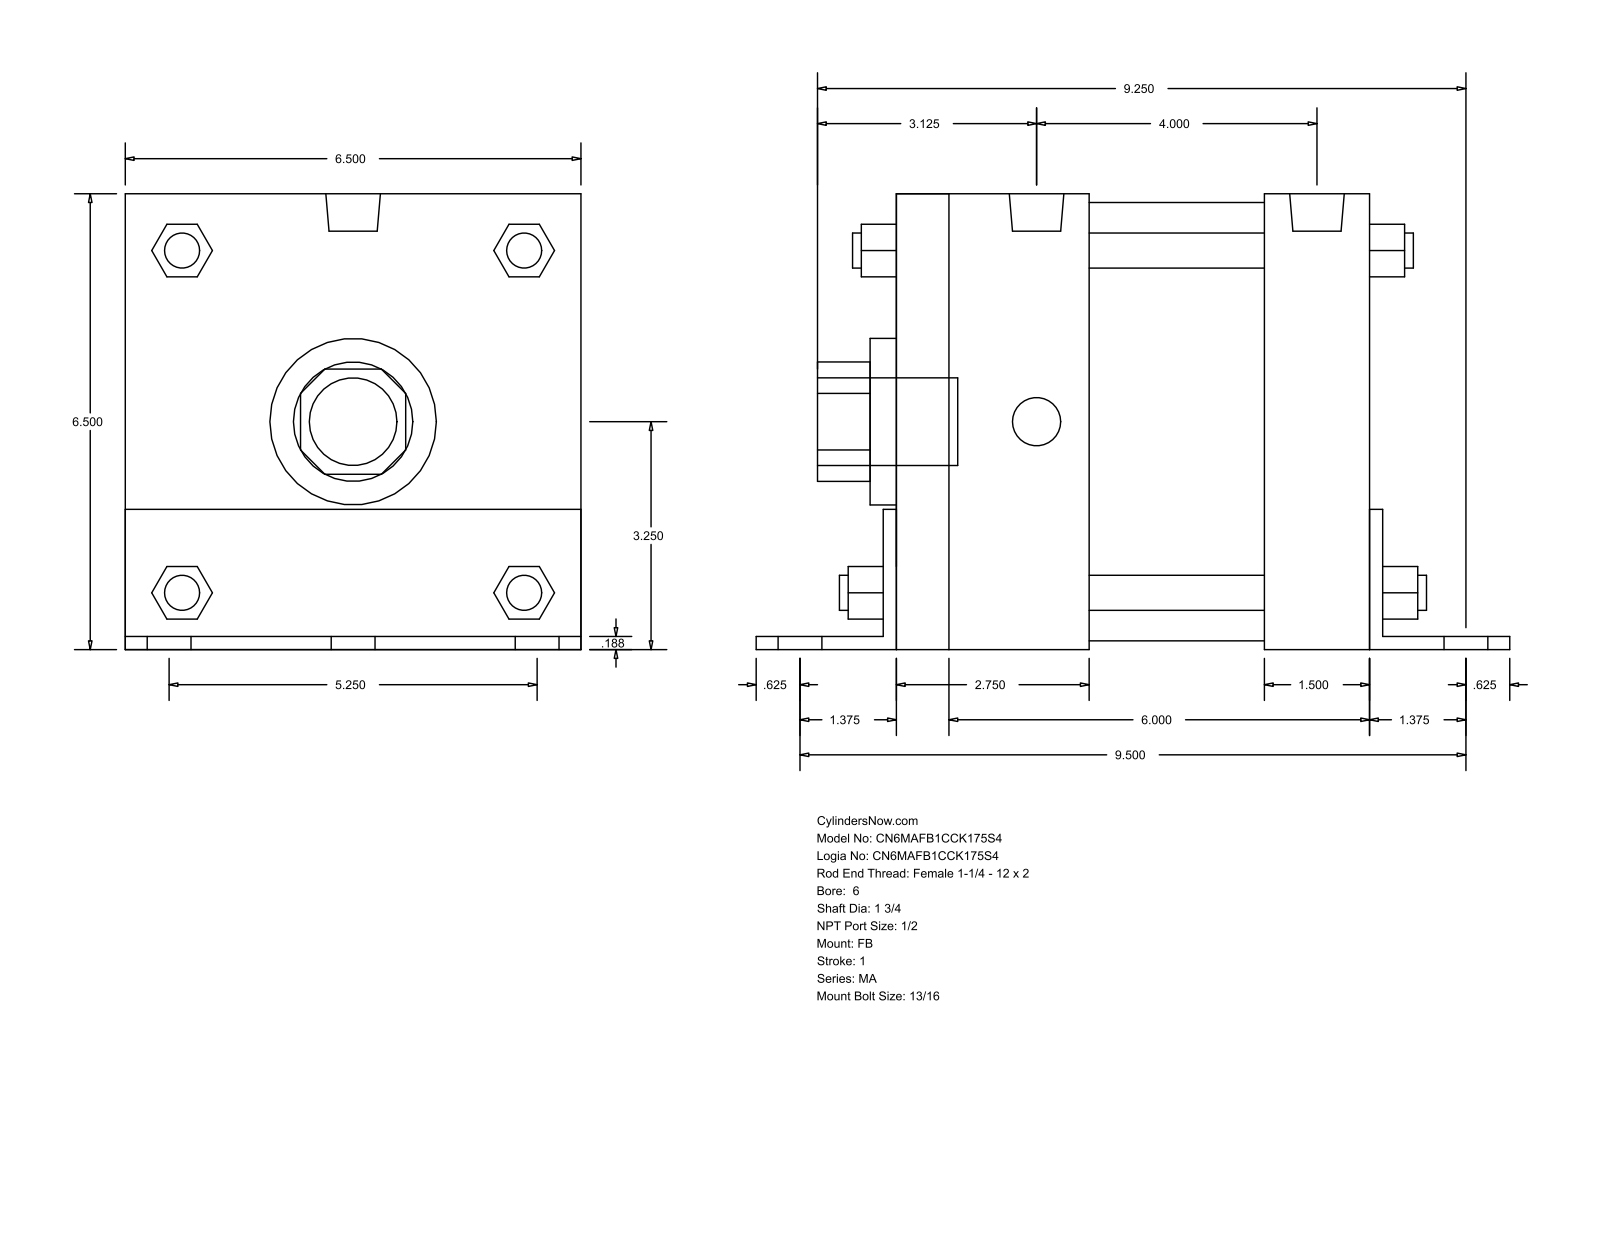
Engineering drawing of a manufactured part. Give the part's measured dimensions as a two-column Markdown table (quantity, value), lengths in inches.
| quantity | value |
| --- | --- |
| part name | MA_FB__0600_1.75 |
| STEP written by | GSSL Pune (CONFIG_CONTROL_DESIGN) |
| units | inches |
| bodies | 0 solids, 140 faces (105 planar, 35 cylindrical, 0 other) |
| overall size | 10.75 × 6.502 × 6.5 |
| round holes (diameter × count) | 1.75 × 1, 2.375 × 1, 6.25 × 1 |
| round bosses / shafts (diameter × count) | 0.813 × 6, 0.687 × 4, 0.5 × 4, 0.778 × 2, 1.25 × 1 |
| partial cylindrical surfaces (radius × count) | 0.852 × 1, 1.262 × 1 |
| main face-to-face distances | 6.5, 0.187, 6.75, 6.502, 6.938, 0.185, 6.315, 7.125, 1.5, 1.687 |
